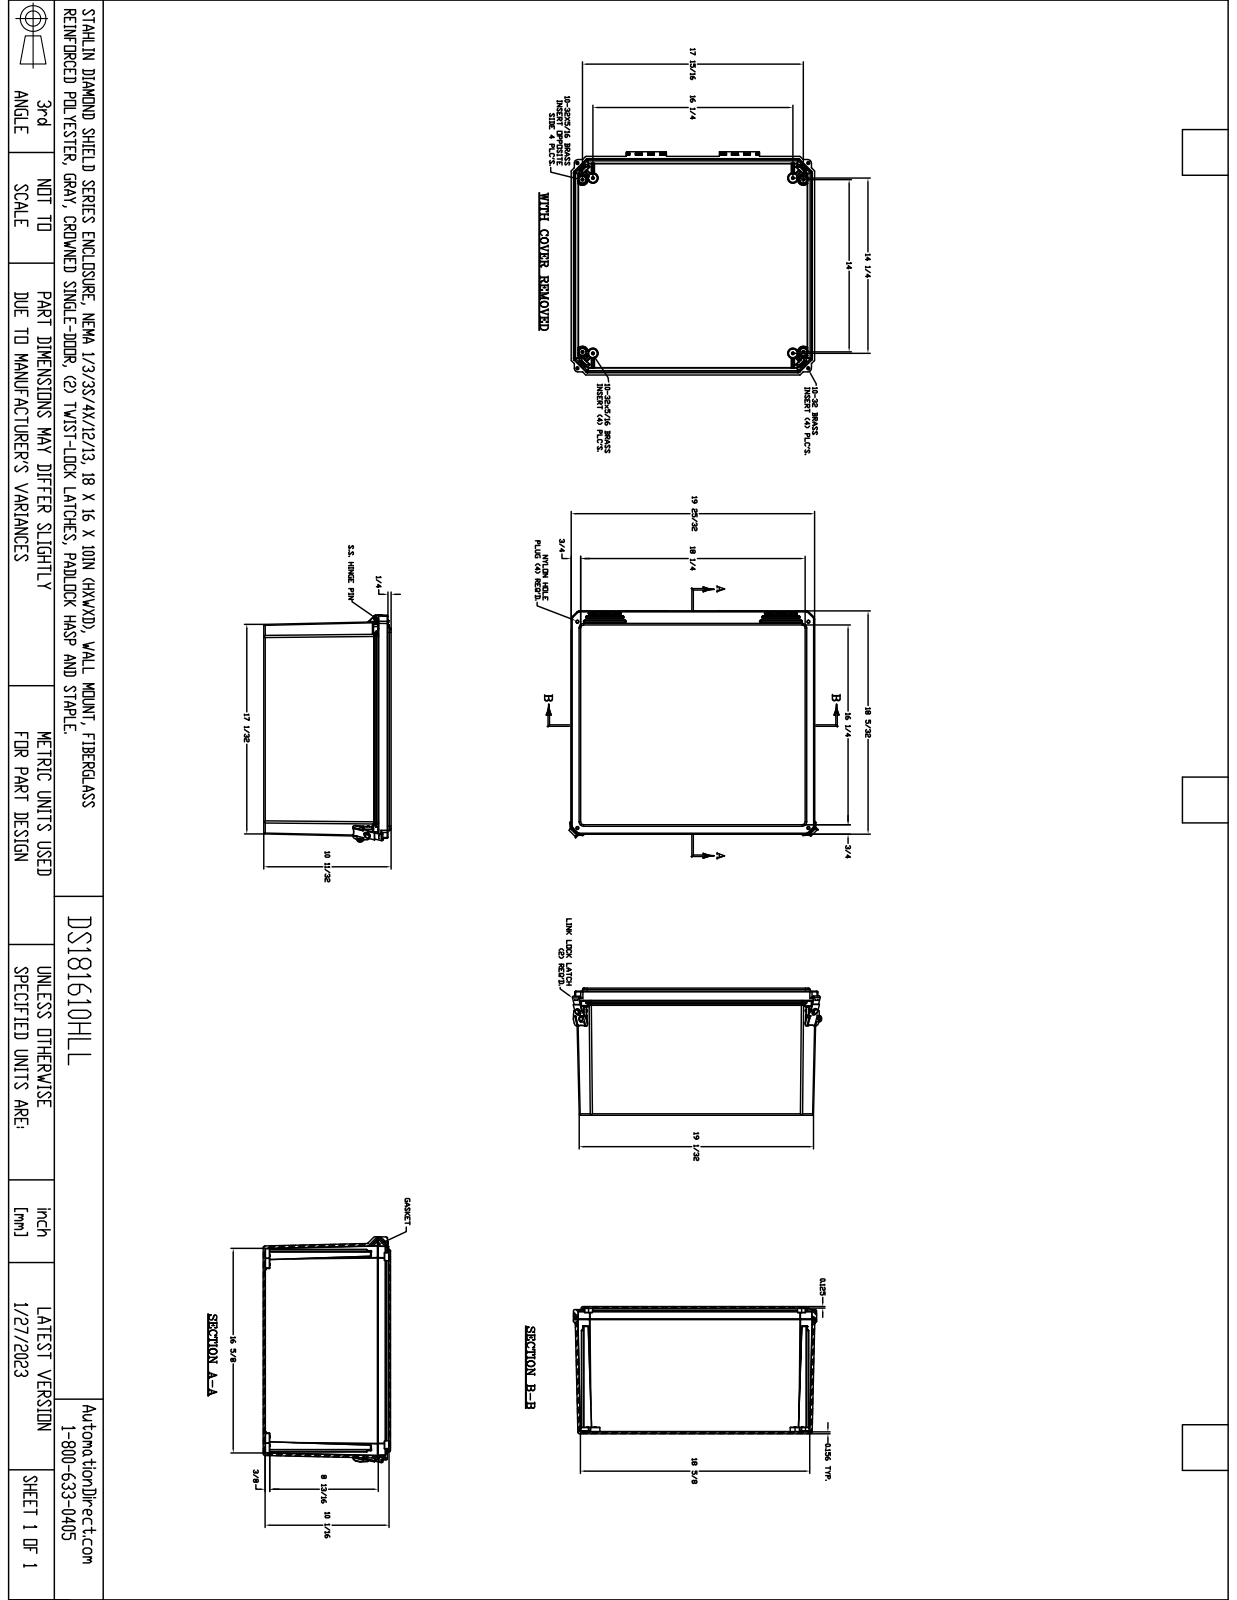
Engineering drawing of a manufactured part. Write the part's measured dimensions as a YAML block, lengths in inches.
part_name: "FR181610HLL"
step_written_by: "SolidWorks 2018 (AUTOMOTIVE_DESIGN)"
units: inches
bodies: {solids: 37, faces: 2353, planar: 824, cylindrical: 920, other: 609}
overall_size: [20.566, 18.545, 10.341]
volume: 258.2
surface_area: 2977
round_holes:
  - {diameter: 0.156, count: 16}
  - {diameter: 0.152, count: 8}
  - {diameter: 0.098, count: 4}
  - {diameter: 0.15, count: 4}
  - {diameter: 0.252, count: 4}
  - {diameter: 0.253, count: 4}
  - {diameter: 0.05, count: 2}
  - {diameter: 0.12, count: 2}
  - {diameter: 0.219, count: 2}
  - {diameter: 0.227, count: 2}
  - {diameter: 0.313, count: 2}
  - {diameter: 0.363, count: 2}
round_bosses_or_shafts:
  - {diameter: 0.246, count: 16}
  - {diameter: 0.209, count: 4}
  - {diameter: 0.2, count: 4}
  - {diameter: 0.6, count: 2}
  - {diameter: 0.435, count: 2}
  - {diameter: 0.135, count: 2}
  - {diameter: 0.05, count: 2}
  - {diameter: 0.135, count: 1}
partial_cylinders:
  - {radius: 0.01, count: 190}
  - {radius: 0.005, count: 88}
  - {radius: 0.02, count: 49}
  - {radius: 0.03, count: 41}
  - {radius: 0.125, count: 34}
  - {radius: 0.039, count: 28}
  - {radius: 0.03, count: 24}
  - {radius: 0.09, count: 24}
face_to_face_distances: [0.125, 0.156, 10.185, 10.341, 0.202, 0.2, 10.217, 10.061, 0.25, 0.125]
hole_center_spacings: [1.783, 15.391, 15.562, 0.429, 0.793, 0.856, 1.446, 14.15]
